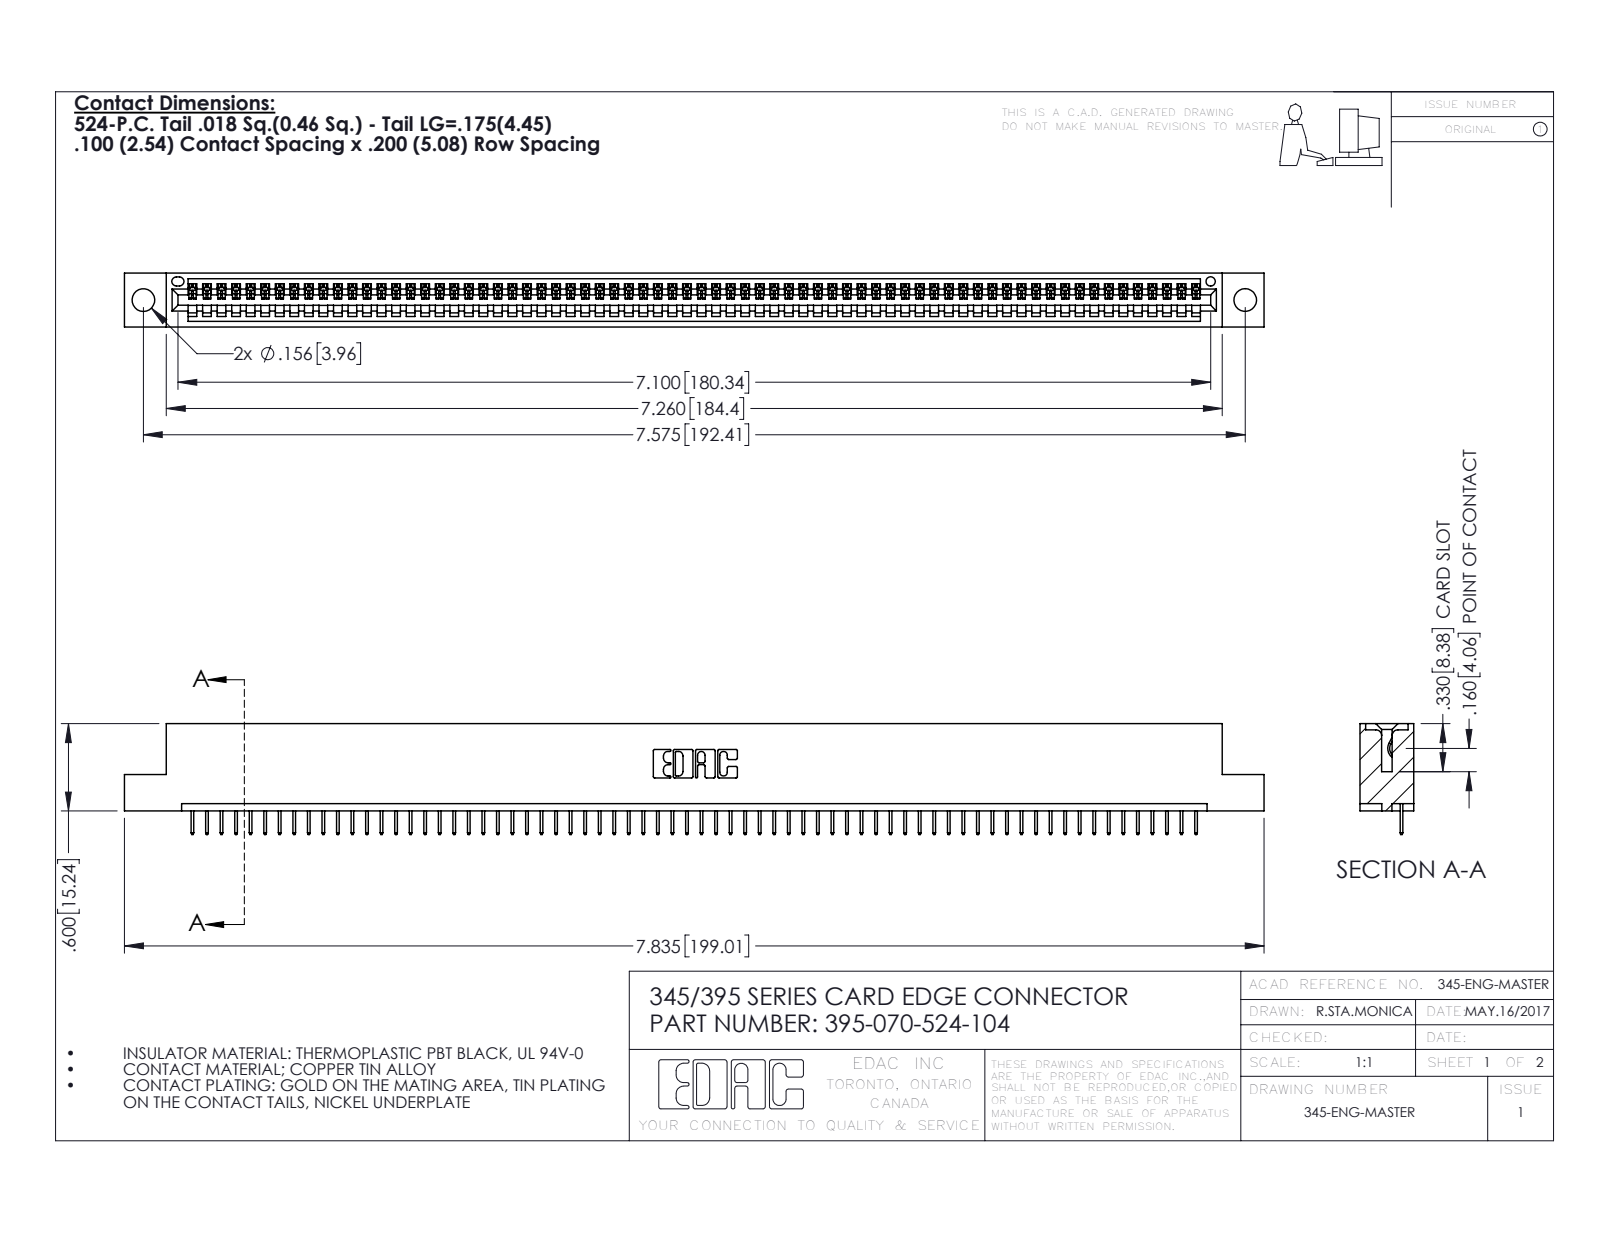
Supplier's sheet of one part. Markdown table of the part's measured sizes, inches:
| quantity | value |
| --- | --- |
| part name | 345-292-001_345-293-124; 395-070-524-104; 345 Part_Flush Mounting Lugs - 0.156 Dia-TH |
| STEP written by | SolidWorks 2016 (CONFIG_CONTROL_DESIGN) |
| units | inches |
| bodies | 71 solids, 4466 faces (3300 planar, 1166 cylindrical, 0 other) |
| overall size | 7.835 × 0.762 × 0.37 |
| volume | 1.145 in³ |
| surface area | 37.58 in² |
| round holes (diameter × count) | 0.156 × 2, 0.064 × 1 |
| partial cylindrical surfaces (radius × count) | 0.006 × 140, 0.01 × 22, 0.007 × 6, 0.031 × 6, 0.026 × 3, 0.031 × 2, 0.04 × 2, 0.014 × 1 |
| main face-to-face distances | 0.298, 0.072, 0.37, 0.2, 0.098, 0.272, 0.025, 0.225, 0.072, 0.149 |
| hole center spacings | 0.27, 7.339, 7.575 |
